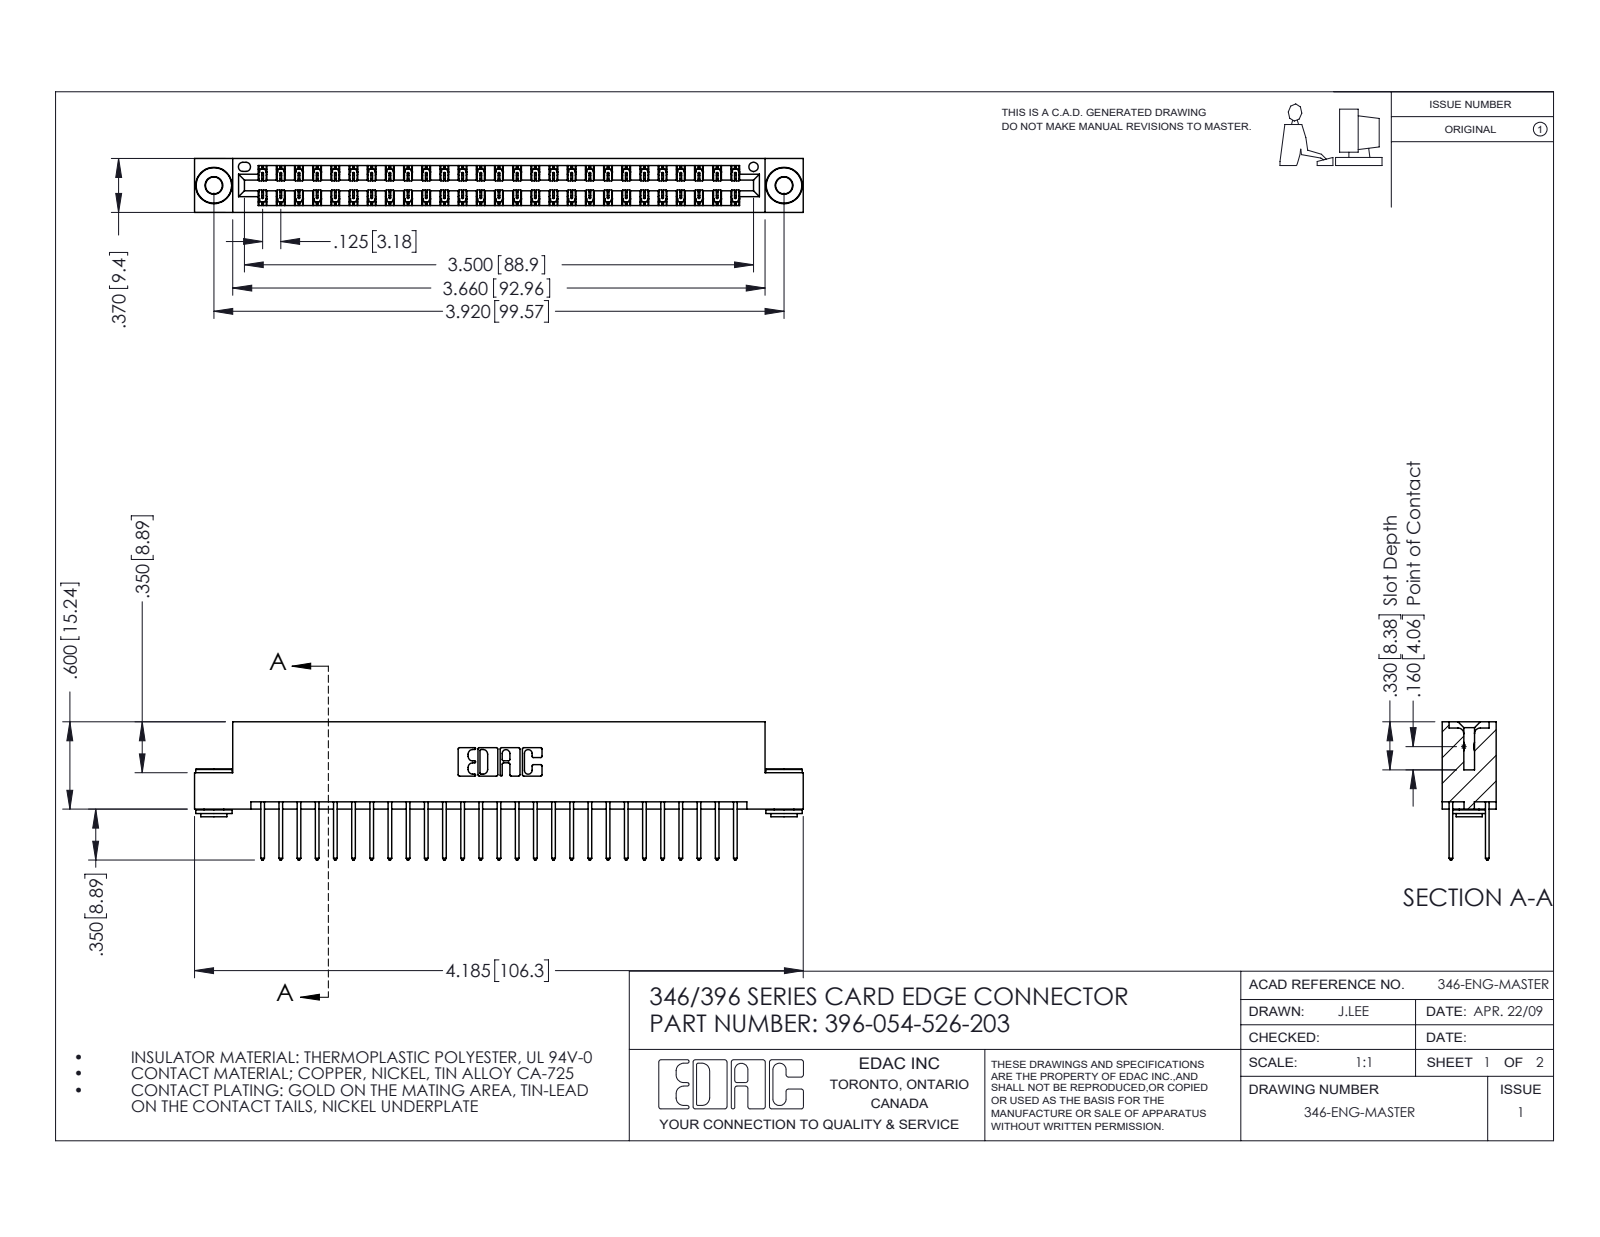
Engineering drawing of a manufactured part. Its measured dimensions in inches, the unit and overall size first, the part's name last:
Units: inches
Overall size (bounding box): 4.185 × 0.95 × 0.37
Round holes (diameter × count): ⌀0.116 ×2, ⌀0.156 ×2, ⌀0.064 ×1
Round bosses / shafts (diameter × count): ⌀0.25 ×2, ⌀0.18 ×2, ⌀0.136 ×2
Partial cylindrical surfaces — rounded edges, fillets, slot ends (radius × count): R0.006 ×81, R0.01 ×54, R0.01 ×22, R0.007 ×6, R0.031 ×6, R0.026 ×3, R0.014 ×2, R0.022 ×2
Main face-to-face distances: 0.048, 0.322, 0.25, 0.37, 0.025, 0.072, 0.298, 0.275, 0.148, 0.222
Hole centre spacings: 0.246, 3.712, 3.92
Volume: 0.632 in³ · Surface area: 22.65 in²
Bodies: 57 solids, 2968 faces (1976 planar, 984 cylindrical, 8 other)
Part name (STEP PRODUCT): 345-292-001_345-293-126; 346 Part_Flush Mounting Lugs - 0.156 Dia-TH; 396-054-526-203; 345-250-002_345-250-002-102
STEP written by: SolidWorks 2016 (CONFIG_CONTROL_DESIGN)
